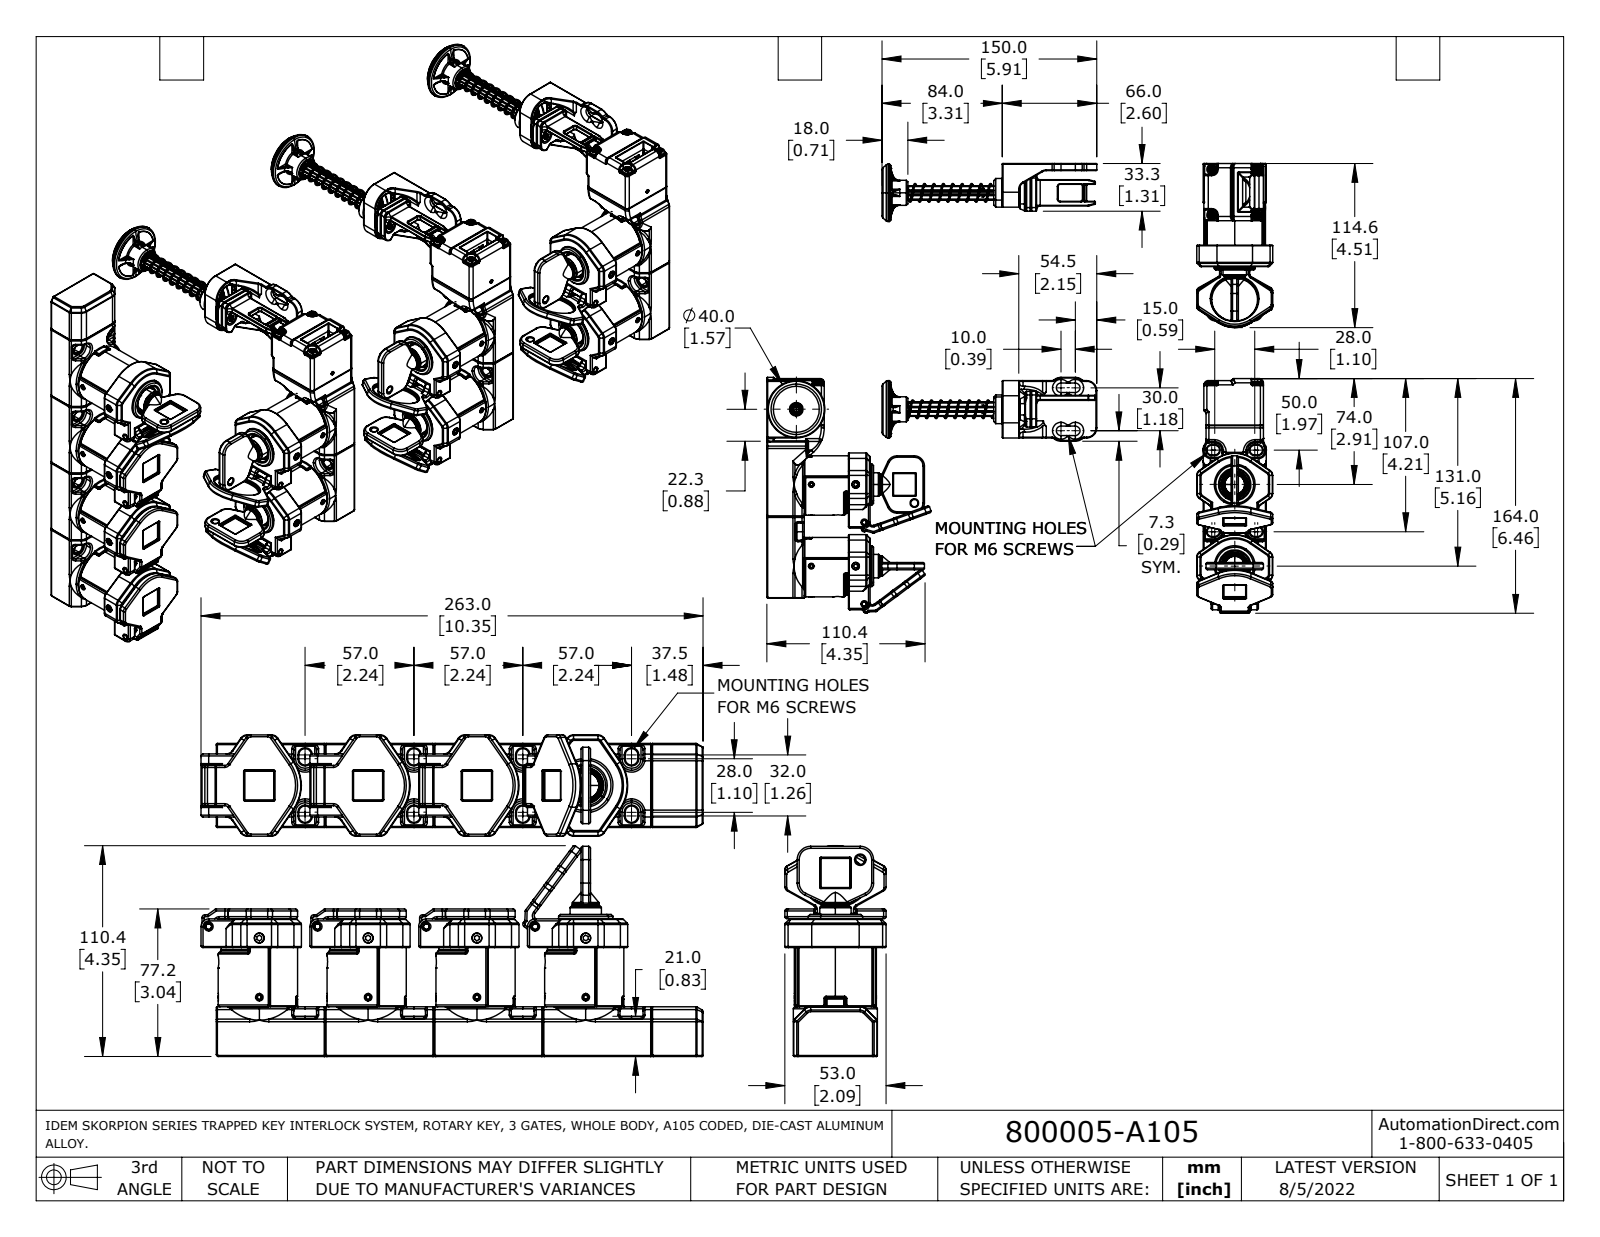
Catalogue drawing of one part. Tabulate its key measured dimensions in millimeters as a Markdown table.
| quantity | value |
| --- | --- |
| part name | 800005-A103_1; 800005-A103_2; 800005-A103; 800005-A103_3 |
| STEP written by | SolidWorks 2021 (AUTOMOTIVE_DESIGN) |
| units | millimeters |
| bodies | 9 solids, 7753 faces (1716 planar, 3248 cylindrical, 2789 other) |
| overall size | 267.4 × 263.5 × 229.2 |
| volume | 872 800 mm³ |
| surface area | 255 600 mm² |
| round holes (diameter × count) | 4.5 × 18, 3.3 × 16, 4.2 × 10, 8 × 10, 3.5 × 9, 40.8 × 6, 3 × 5, 4 × 4, 5 × 4, 2.2 × 2, 2.5 × 2, 6 × 2 |
| round bosses / shafts (diameter × count) | 1.3 × 18, 7.4 × 12, 3.9 × 10, 3.5 × 7, 40 × 6, 3.1 × 6, 38 × 4, 7 × 4 |
| partial cylindrical surfaces (radius × count) | 0.5 × 1015, 1 × 553, 0.3 × 100, 2 × 81, 4 × 51, 3 × 32, 1.5 × 30, 3.3 × 24 |
| main face-to-face distances | 77.2, 44, 3, 1, 76.2, 57, 180.7, 224.7, 5, 20.2 |
| hole center spacings | 57, 20.9, 114, 43.8, 63.5, 73.8, 28, 171 |
